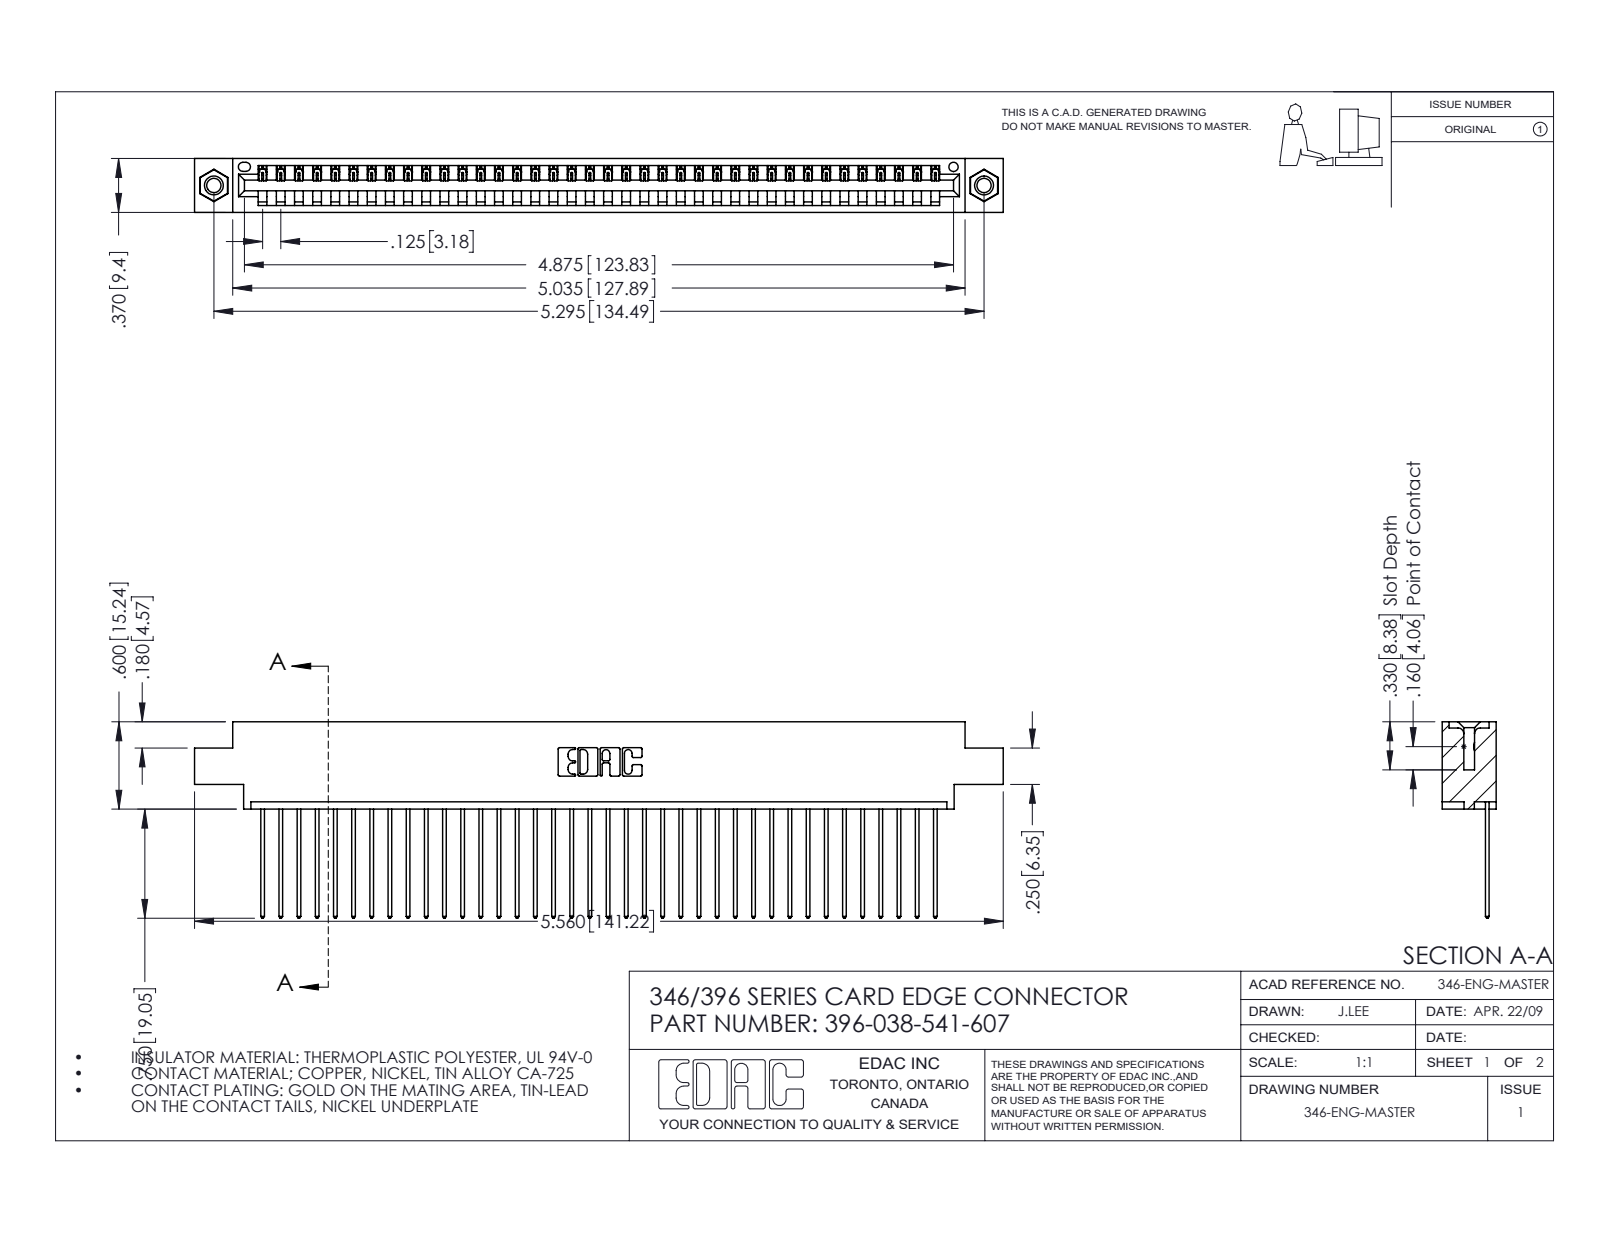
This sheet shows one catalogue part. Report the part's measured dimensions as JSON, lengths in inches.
{"part_name": "345-292-001_345-293-141; 345-250-001_345-250-005-103; 346 Part_0.170 Offset - 0.156 Dia-TI; 396-038-541-607", "step_written_by": "SolidWorks 2016 (CONFIG_CONTROL_DESIGN)", "units": "inches", "bodies": {"solids": 41, "faces": 2390, "planar": 1632, "cylindrical": 742, "other": 16}, "overall_size": [5.56, 1.35, 0.37], "volume_in3": 0.821, "surface_area_in2": 27.45, "round_holes": [[0.098, 2], [0.125, 2], [0.156, 2], [0.064, 1]], "round_bosses_or_shafts": [[0.155, 2]], "partial_cylinders_radius": [[0.006, 76], [0.01, 76], [0.01, 22], [0.007, 6], [0.031, 6], [0.026, 3], [0.031, 2], [0.04, 2]], "face_to_face_distances": [0.048, 0.322, 0.37, 0.25, 0.072, 0.298, 0.025, 0.222, 0.148, 0.1], "hole_center_spacings": [0.246, 5.086, 5.295]}
